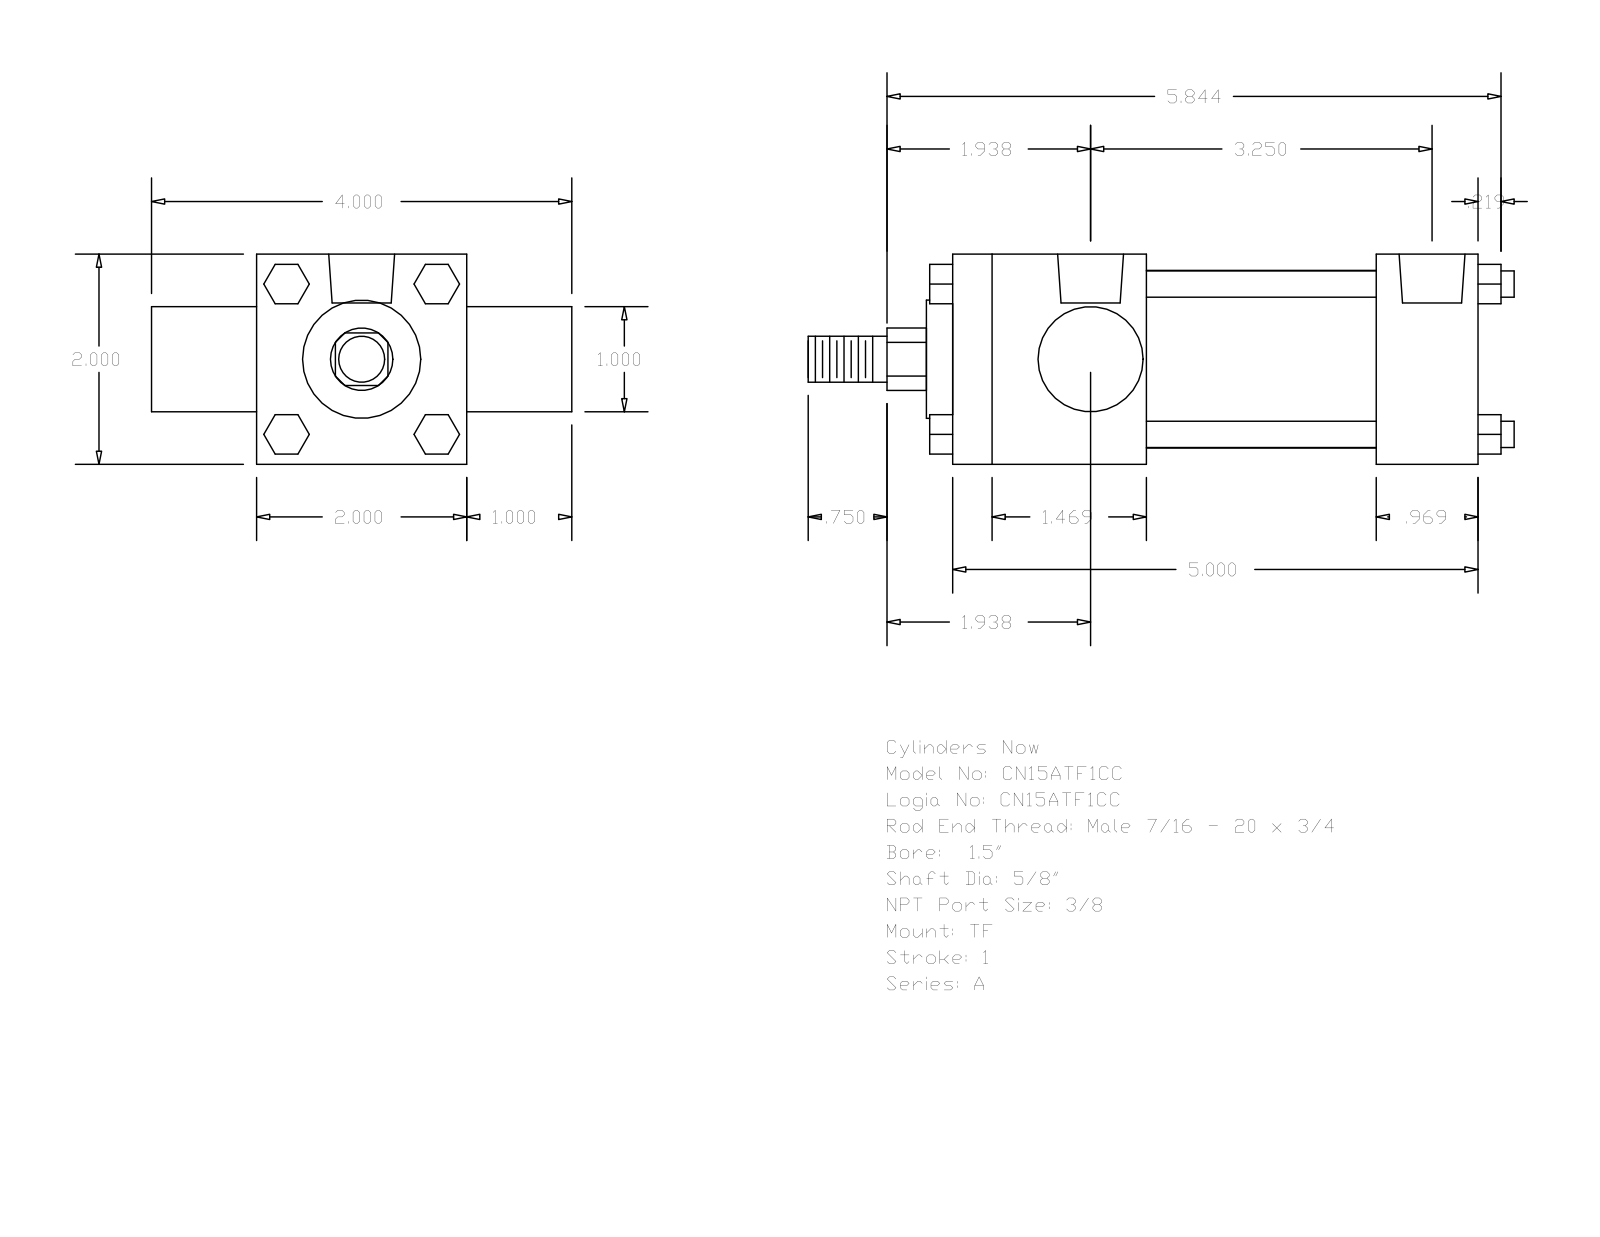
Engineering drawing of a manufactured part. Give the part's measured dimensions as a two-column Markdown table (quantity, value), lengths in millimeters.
| quantity | value |
| --- | --- |
| part name | A_TF__0150_0.625 |
| STEP written by | GSSL Pune (CONFIG_CONTROL_DESIGN) |
| units | millimeters |
| bodies | 0 solids, 120 faces (92 planar, 28 cylindrical, 0 other) |
| overall size | 170.66 × 101.6 × 50.8 |
| round holes (diameter × count) | 5.56 × 3, 15.93 × 2 |
| round bosses / shafts (diameter × count) | 6.35 × 4, 42.93 × 1, 28.57 × 1, 25.4 × 1, 15.88 × 1, 11.11 × 1 |
| partial cylindrical surfaces (radius × count) | 7.54 × 1 |
| main face-to-face distances | 50.8, 127, 25.4, 76.2, 46.83, 102.39, 55.56, 80.17, 24.61, 101.6 |
| hole center spacings | 3.97, 78.58, 74.61, 82.55 |
